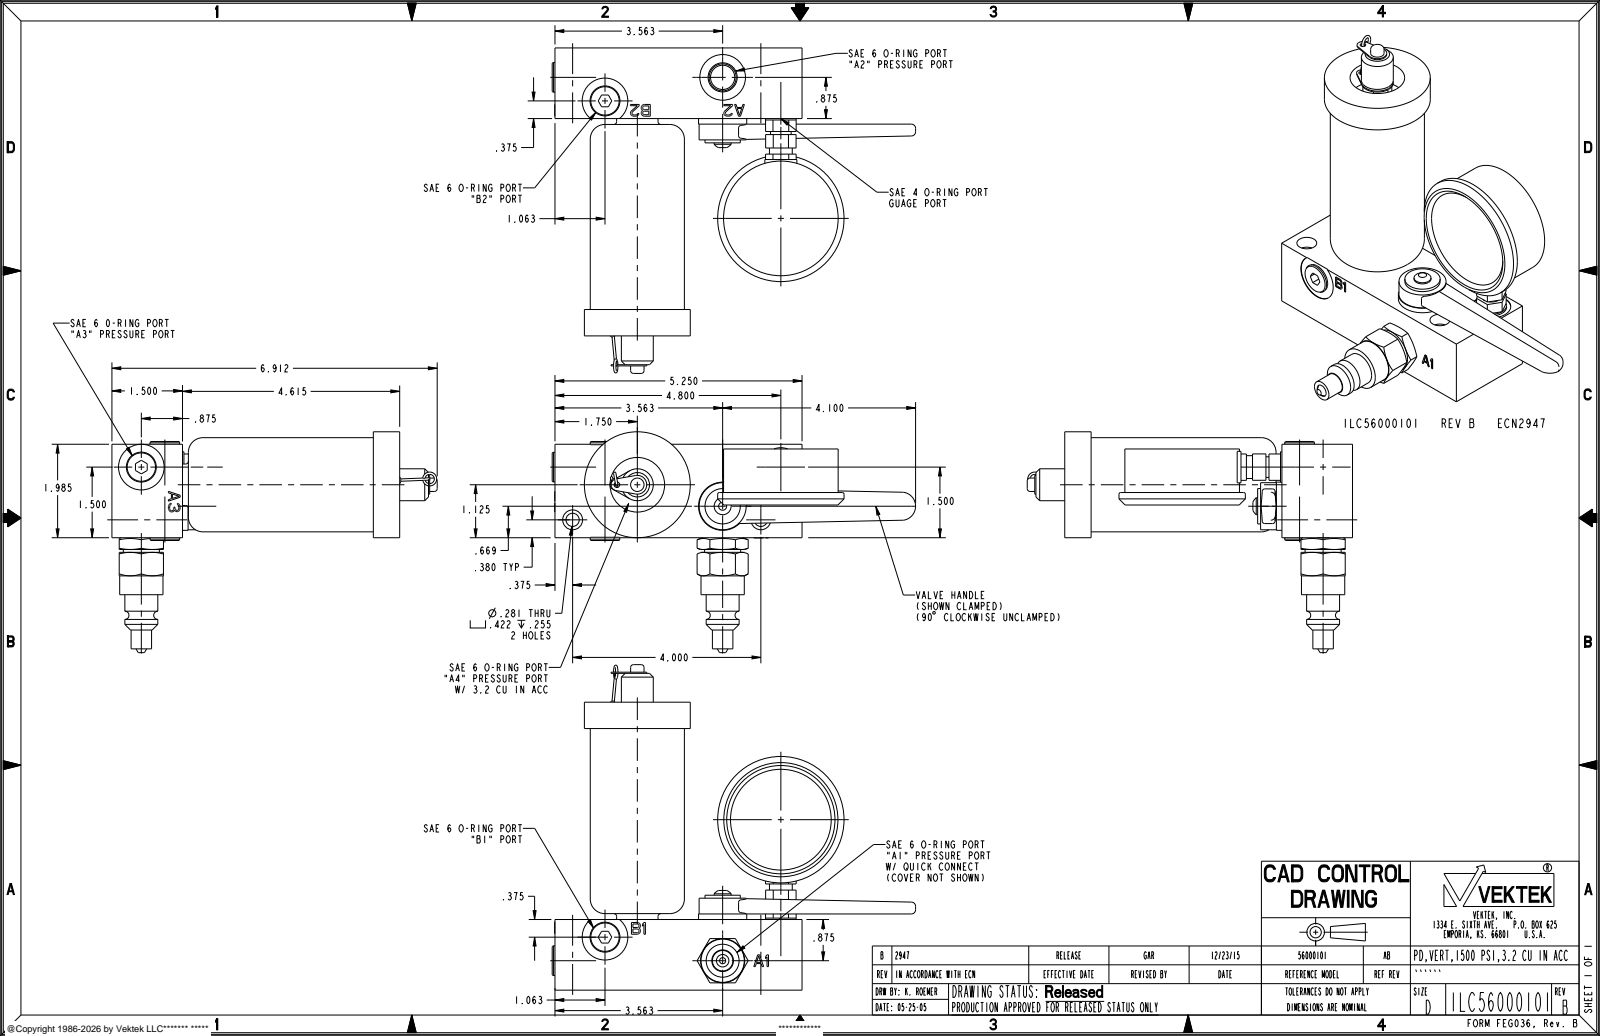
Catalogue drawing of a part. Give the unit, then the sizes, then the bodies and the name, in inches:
Units: inches
Overall size (bounding box): 7.722 × 6.912 × 4.69
Round holes (diameter × count): ⌀0.515 ×4, ⌀0.97 ×3, ⌀0.118 ×2, ⌀0.281 ×2, ⌀0.422 ×2, ⌀0.12 ×1, ⌀0.265 ×1, ⌀0.392 ×1, ⌀0.442 ×1, ⌀0.498 ×1, ⌀0.825 ×1, ⌀1.16 ×1
Round bosses / shafts (diameter × count): ⌀0.563 ×4, ⌀0.51 ×2, ⌀2.685 ×1, ⌀2.435 ×1, ⌀2.25 ×1, ⌀2 ×1, ⌀1.024 ×1, ⌀1 ×1
Partial cylindrical surfaces — rounded edges, fillets, slot ends (radius × count): R0.09 ×2, R0.108 ×1, R0.125 ×1, R0.2 ×1, R0.3 ×1, R0.485 ×1
Main face-to-face distances: 1.5, 1.985, 0.1, 1.885, 1.21, 1.11, 0.775, 6.115, 4.615, 5.25
Hole centre spacings: 0.039, 0.433, 0.472, 1.171, 1.198, 1.201, 1.564, 2.55
Volume: 37.03 in³ · Surface area: 139.6 in²
Bodies: 5 solids, 613 faces (396 planar, 113 cylindrical, 104 other)
Part name (STEP PRODUCT): ILC56000101
STEP written by: PRO/ENGINEER BY PARAMETRIC TECHNOLOGY CORPORATION, 2013320 (AUTOMOTIVE_DESIGN)
